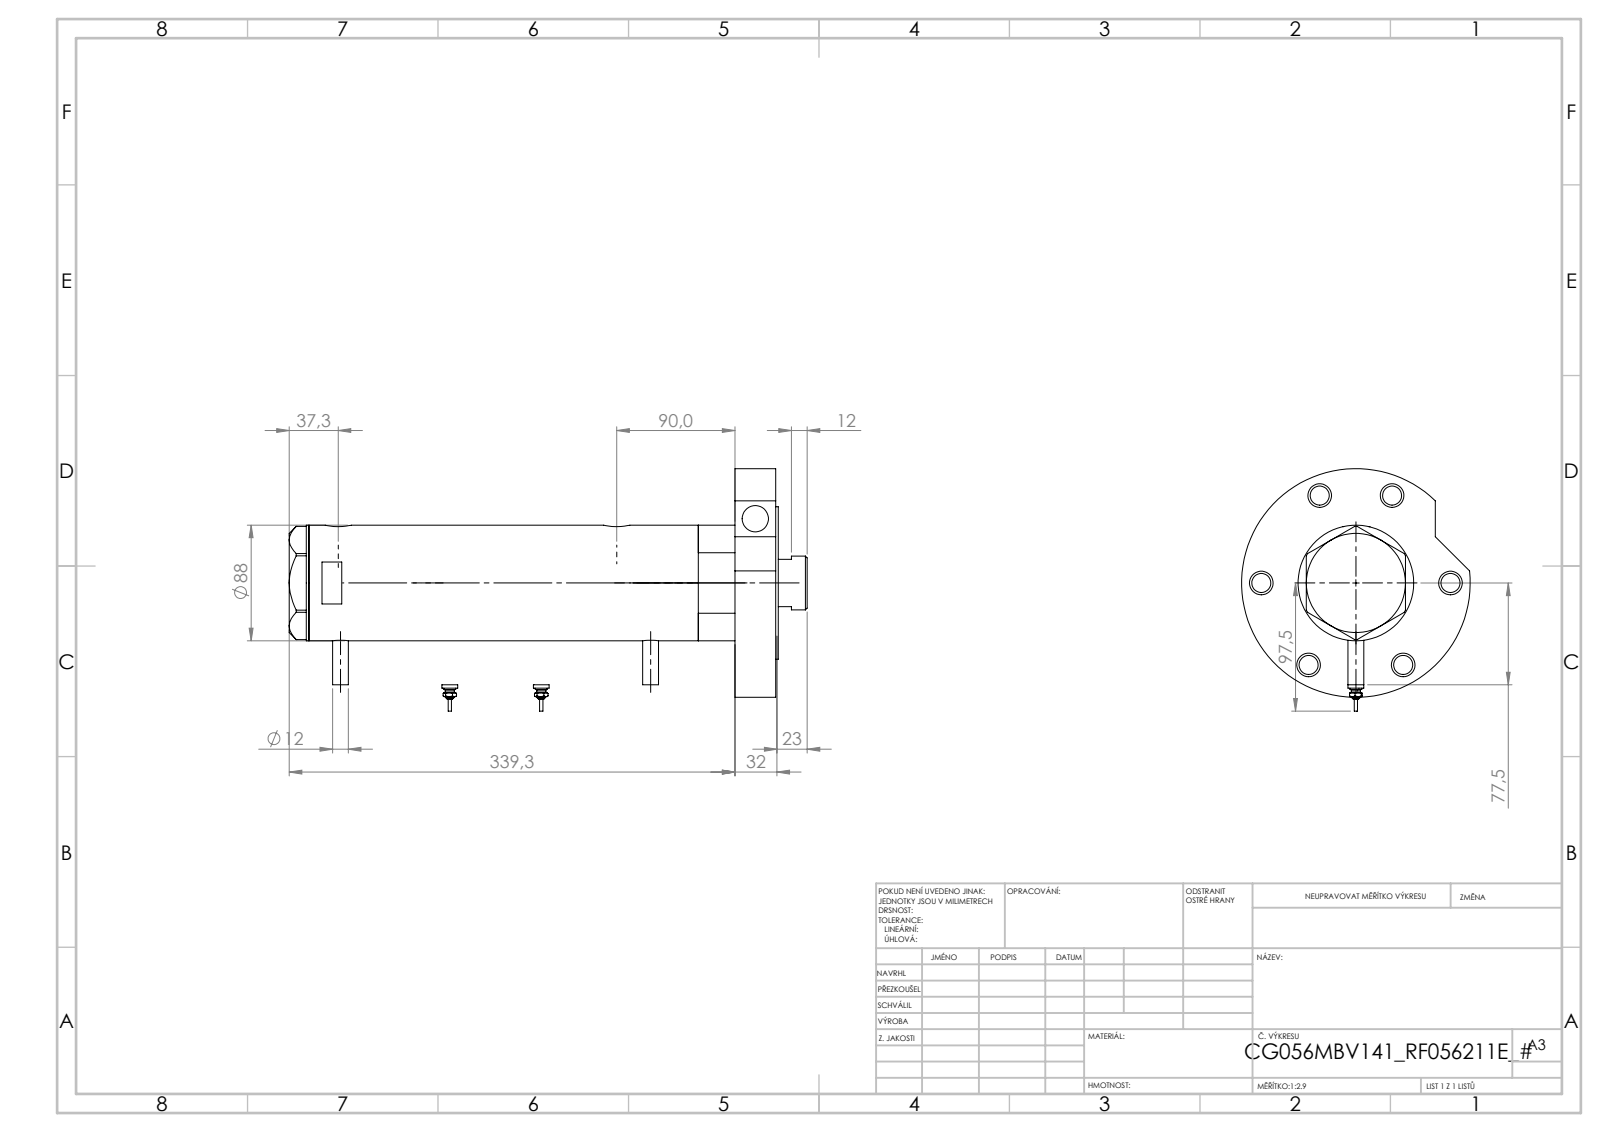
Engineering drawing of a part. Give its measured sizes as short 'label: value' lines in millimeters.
name: V270CG_MIDDLE; V270CG_FRONT; Switch; V270CG_VC (+2 more)
written by: SolidWorks 2019 (CONFIG_CONTROL_DESIGN)
unit: mm
bodies: 7 solids, 257 faces (91 planar, 102 cylindrical, 64 other)
size: 394.3 × 184.5 × 174
volume: 2 571 000 mm³; area: 361 087 mm²
holes: 7× ⌀14.5, 6× ⌀18, 3× ⌀20, 2× ⌀12.5, 2× ⌀13.16, 1× ⌀42, 1× ⌀43.5, 1× ⌀56, 1× ⌀60, 1× ⌀75, 1× ⌀80
bosses: 4× ⌀12, 2× ⌀9, 2× ⌀7, 2× ⌀4.5, 2× ⌀2.5, 1× ⌀174, 1× ⌀116, 1× ⌀88
face distances: 31, 2, 357.3, 324.3, 355.3, 33, 234.4, 89.9, 120.9, 122.9
hole spacings: 72, 80, 119.73, 124.71, 129.15, 143.69, 1.7, 25.8
